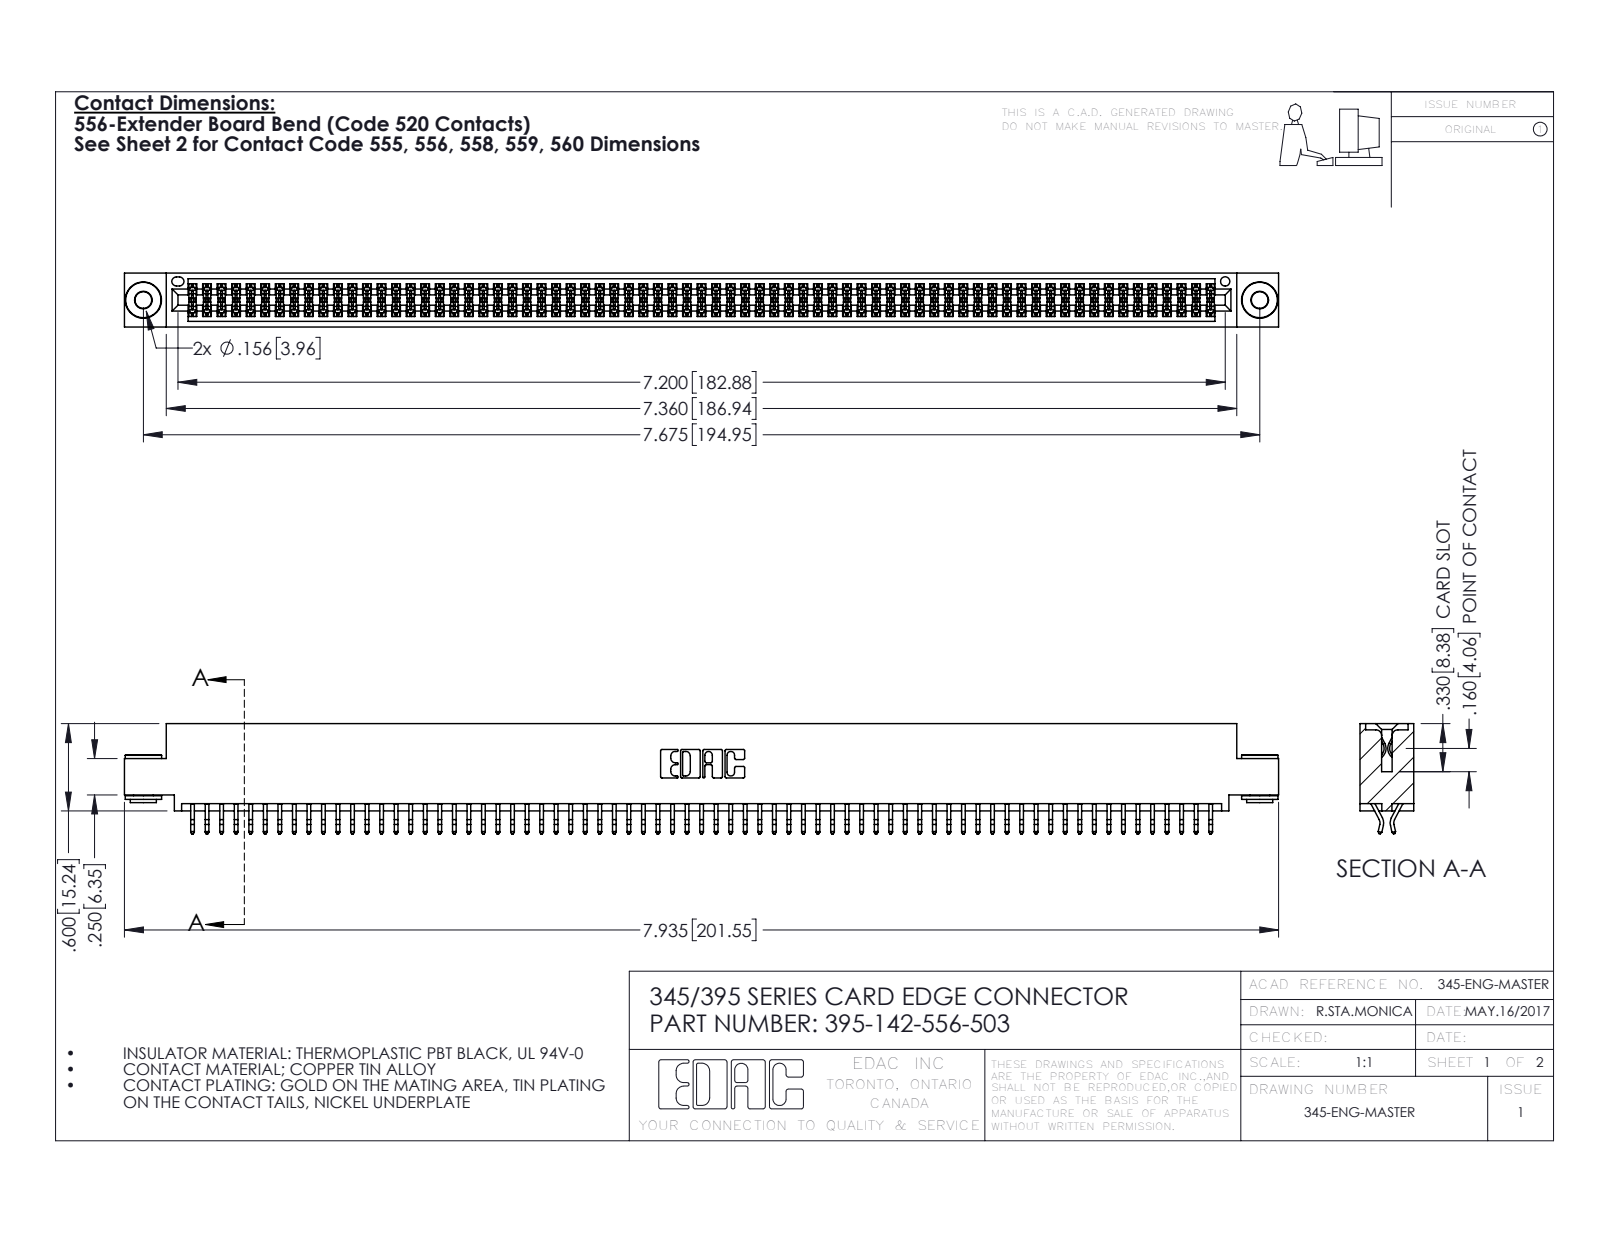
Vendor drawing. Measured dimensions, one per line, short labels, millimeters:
name: 395-142-556-503; 345-250-002_345-250-002-102; 345 Part_0.110 Offset - 0.156 Dia-TH; 345-292-001_556 Tail
written by: SolidWorks 2016 (CONFIG_CONTROL_DESIGN)
unit: mm
bodies: 145 solids, 8120 faces (5348 planar, 2764 cylindrical, 8 other)
size: 201.5 × 19.2 × 9.4
volume: 19 800 mm³; area: 29 990 mm²
holes: 2× ⌀2.9, 2× ⌀4, 1× ⌀1.6
bosses: 2× ⌀6.4, 2× ⌀4.6, 2× ⌀3.5
rounds: 213× R0.2, 22× R0.3, 6× R0.2, 6× R0.8, 3× R0.7, 2× R0.3, 2× R0.4, 2× R0.5
face distances: 1.8, 7.6, 9.4, 0.6, 5.1, 2.5, 6.9, 5.7, 4.4, 3.8
hole spacings: 6.9, 189, 194.9
